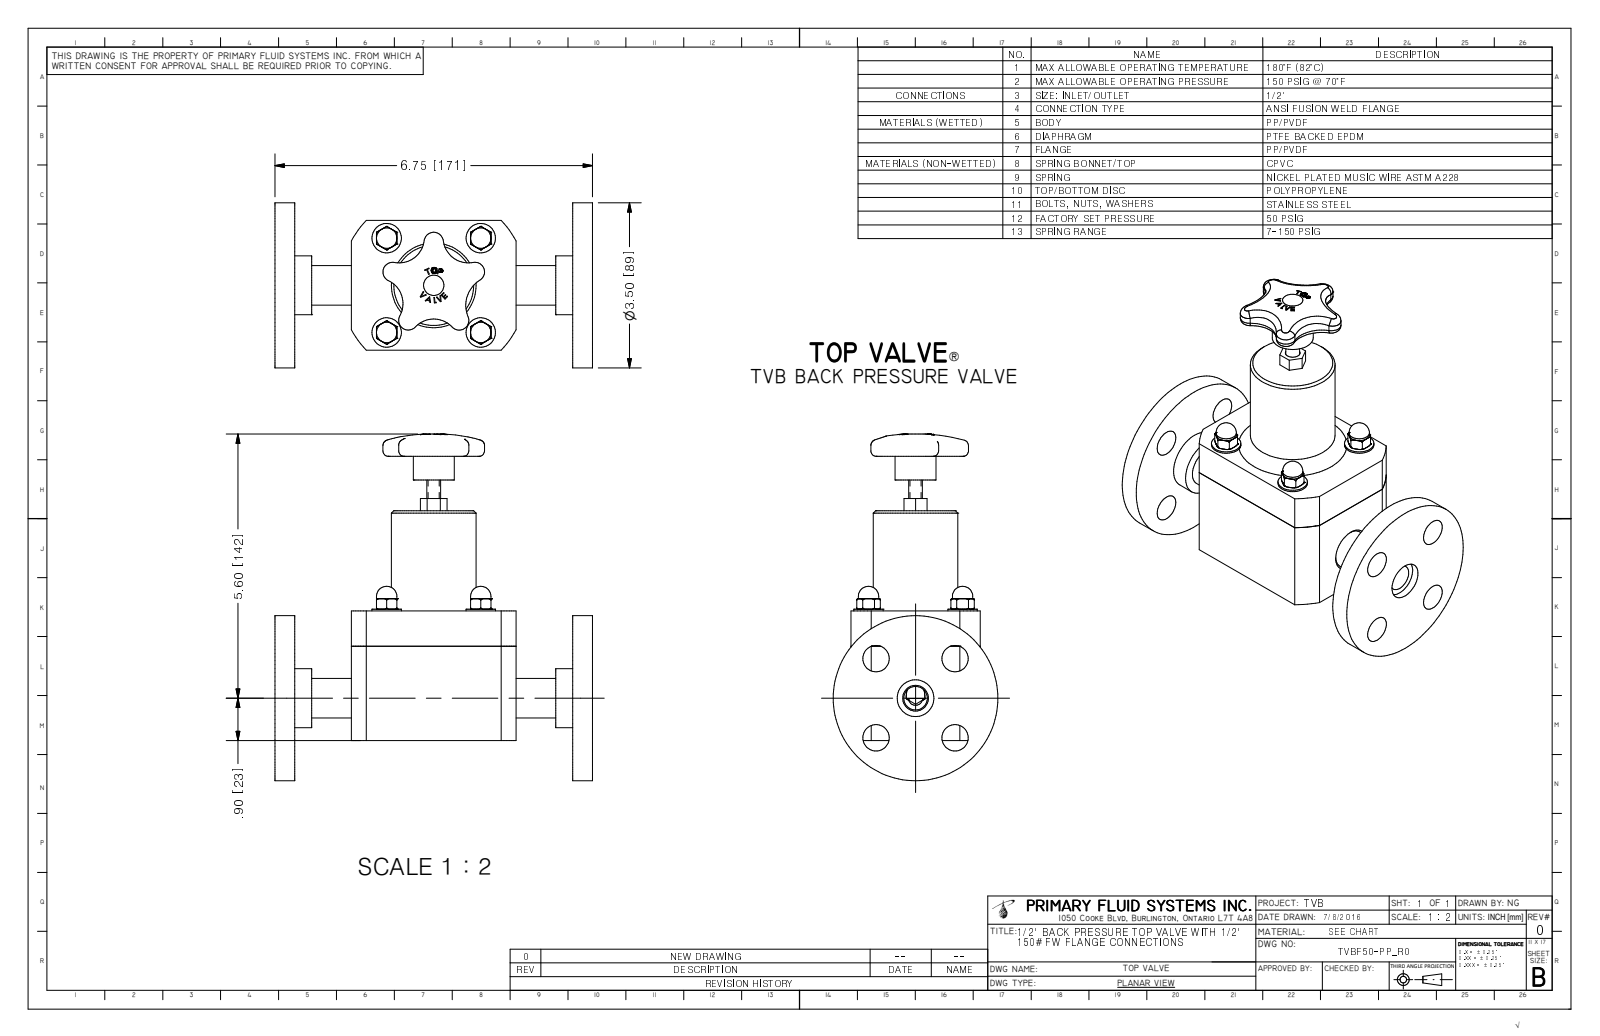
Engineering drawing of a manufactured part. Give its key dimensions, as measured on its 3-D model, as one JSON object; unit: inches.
{"part_name": "TVBF50-PP_R0", "step_written_by": "Autodesk Inventor 2009 (AUTOMOTIVE_DESIGN)", "units": "inches", "bodies": {"solids": 1, "faces": 361, "planar": 152, "cylindrical": 61, "other": 148}, "overall_size": [7.352, 6.75, 3.5], "volume_in3": 40.84, "surface_area_in2": 140, "round_holes": [[0.175, 4], [0.56, 4], [0.546, 1], [0.78, 1]], "round_bosses_or_shafts": [[0.625, 4], [0.433, 4], [0.375, 4], [3.5, 1], [1.8, 1], [1.25, 1], [0.87, 1], [0.84, 1]], "partial_cylinders_radius": [[0.085, 5], [0.205, 5], [0.536, 4], [0.656, 4], [0.625, 1], [0.745, 1], [1.988, 1]], "face_to_face_distances": [0.42, 6.33, 1.625, 5.125, 1.205, 4.705, 6.75, 2.75, 5.91, 3.5], "hole_center_spacings": [1.188, 1.68, 2, 2.375, 2.828]}
